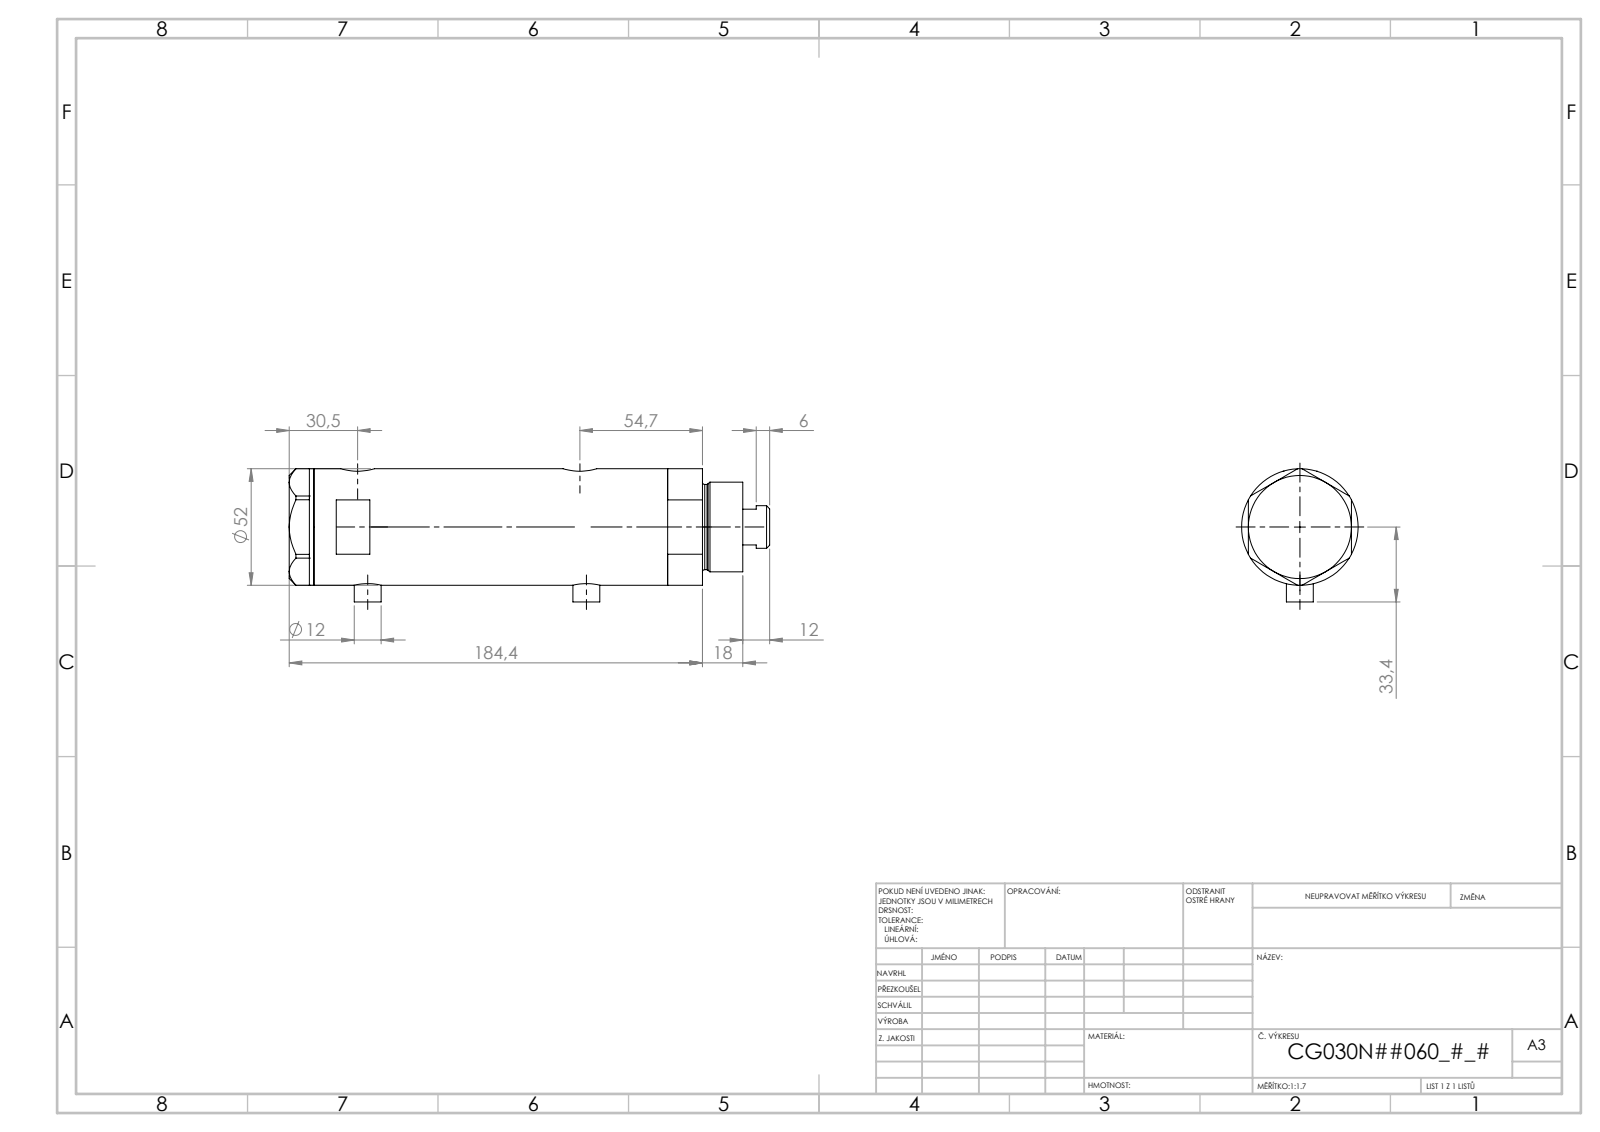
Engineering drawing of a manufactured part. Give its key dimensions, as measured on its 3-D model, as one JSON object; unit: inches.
{"part_name": "V270CG_FRONT; V270CG_MIDDLE; V270CG_BACK; V270CG_VC", "step_written_by": "SolidWorks 2019 (CONFIG_CONTROL_DESIGN)", "units": "inches", "bodies": {"solids": 4, "faces": 140, "planar": 67, "cylindrical": 53, "other": 20}, "overall_size": [8.229, 2.091, 2.047], "volume_in3": 22.66, "surface_area_in2": 130.7, "round_holes": [[0.197, 2], [0.383, 2], [0.492, 2], [0.591, 2], [0.256, 1], [0.787, 1], [0.846, 1], [1.181, 1], [1.299, 1], [1.732, 1]], "round_bosses_or_shafts": [[0.472, 2], [2.047, 1], [1.575, 1], [1.496, 1], [0.748, 1]], "face_to_face_distances": [0.937, 4.904, 1.811, 0.433, 0.433, 4.47, 4.47, 6.337, 5.904, 5.903], "hole_center_spacings": [0.114, 0.177, 3.415, 3.53, 3.593, 3.707, 0.114, 0.115]}
